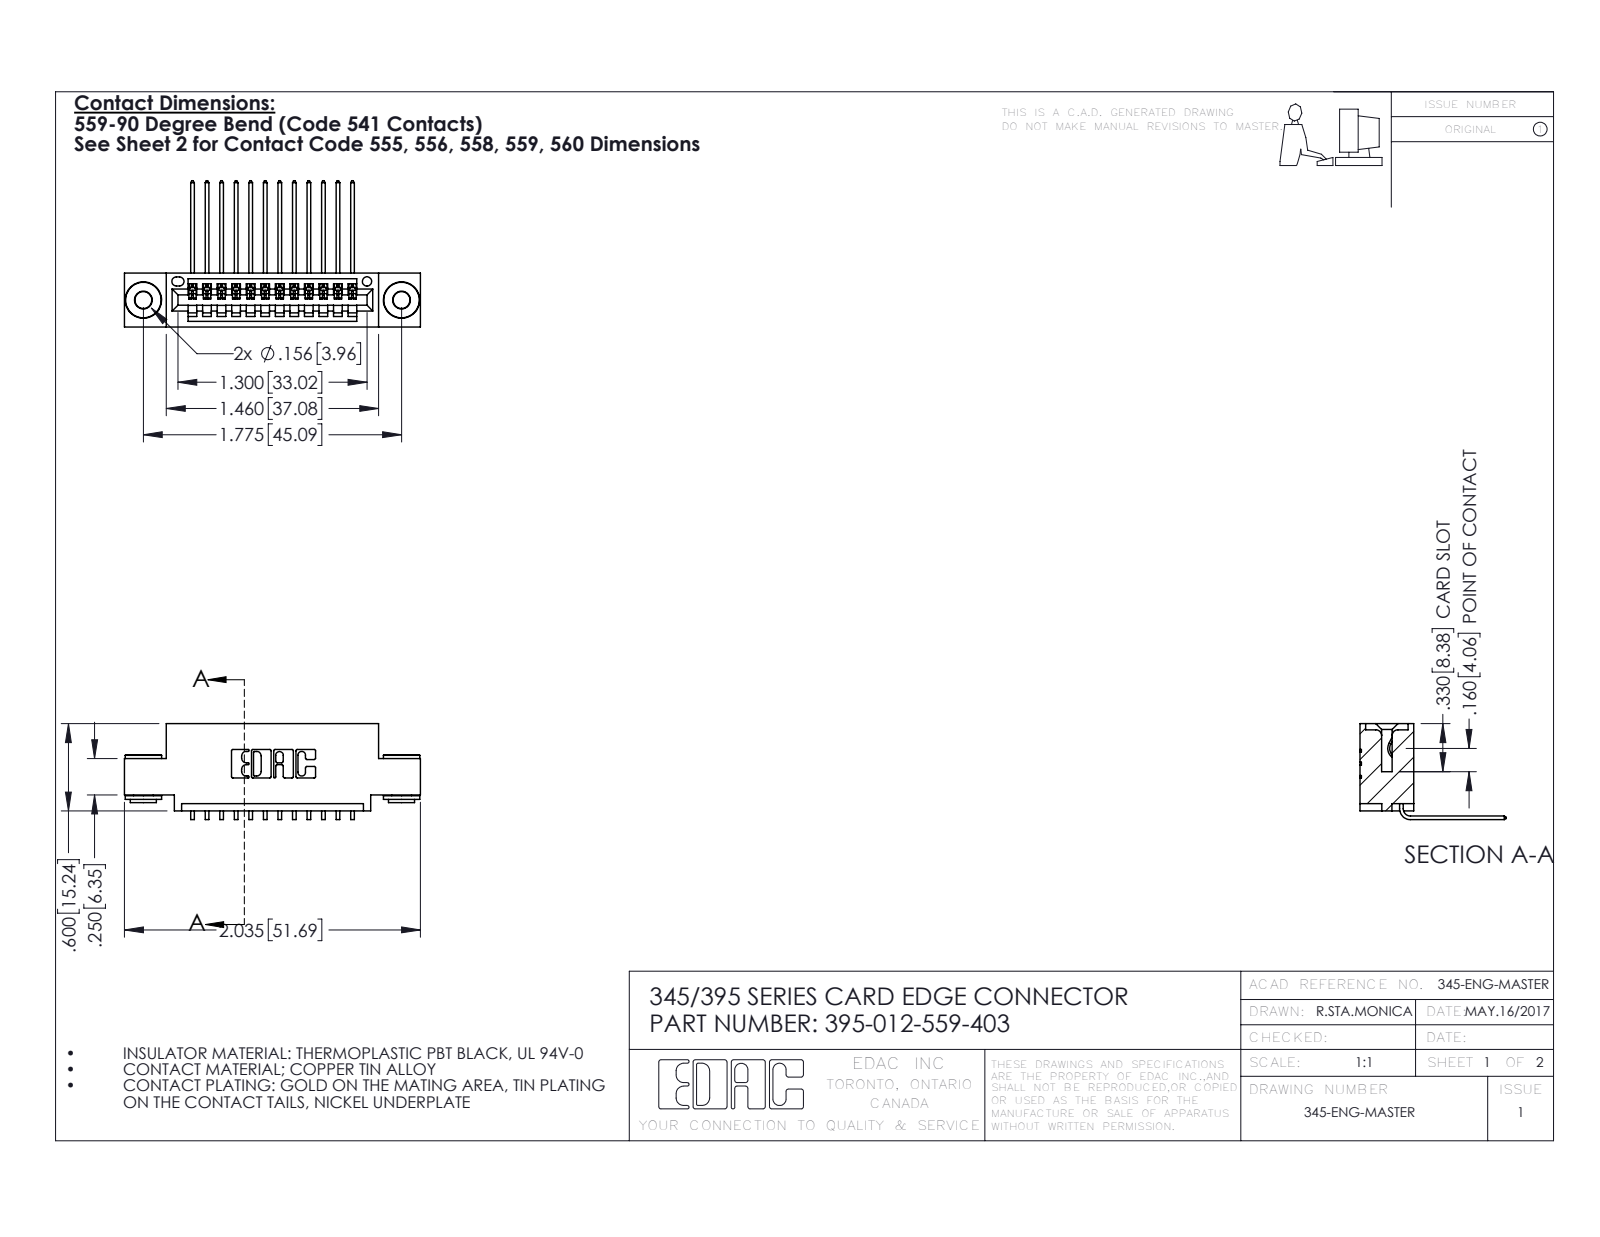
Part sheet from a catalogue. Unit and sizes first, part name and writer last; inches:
Units: inches
Overall size (bounding box): 2.035 × 1.005 × 0.659
Round holes (diameter × count): ⌀0.116 ×2, ⌀0.156 ×2, ⌀0.064 ×1
Round bosses / shafts (diameter × count): ⌀0.25 ×2, ⌀0.18 ×2, ⌀0.136 ×2
Partial cylindrical surfaces — rounded edges, fillets, slot ends (radius × count): R0.006 ×24, R0.01 ×22, R0.007 ×6, R0.031 ×6, R0.026 ×3, R0.031 ×2, R0.04 ×2, R0.014 ×1
Main face-to-face distances: 0.072, 0.298, 0.2, 0.37, 0.025, 0.098, 0.272, 0.1, 0.16, 0.3
Hole centre spacings: 0.27, 1.543, 1.775
Volume: 0.284 in³ · Surface area: 9.769 in²
Bodies: 15 solids, 888 faces (598 planar, 282 cylindrical, 8 other)
Part name (STEP PRODUCT): 345-292-001_558 559 Tail - 1; 345 Part_0.110 Offset - 0.156 Dia-TH; 395-012-559-403; 345-250-002_345-250-002-102
STEP written by: SolidWorks 2016 (CONFIG_CONTROL_DESIGN)
